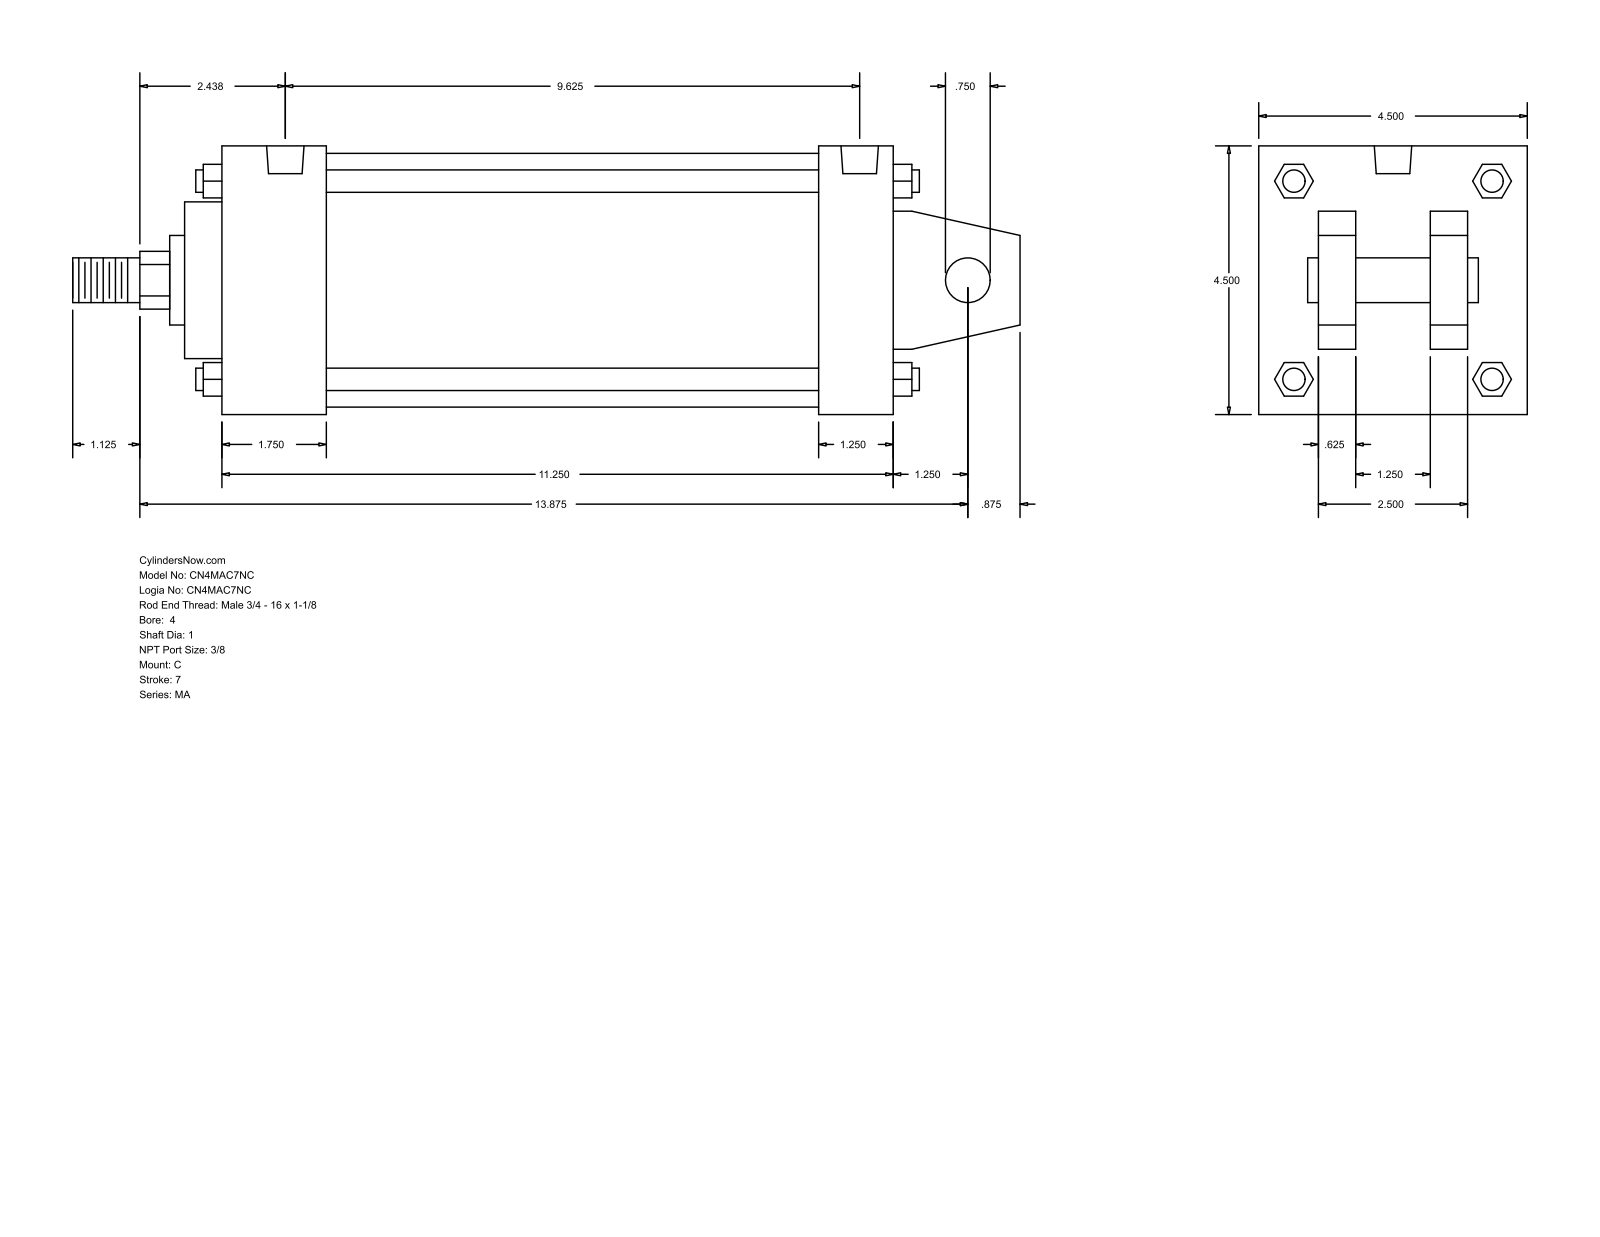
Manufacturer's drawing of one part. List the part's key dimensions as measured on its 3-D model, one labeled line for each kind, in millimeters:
Part name (STEP PRODUCT): MA_C__0400_1
STEP written by: GSSL Pune (CONFIG_CONTROL_DESIGN)
Units: millimetres
Bodies: 0 solids, 141 faces (109 planar, 32 cylindrical, 0 other)
Overall size (bounding box): 403.23 × 114.3 × 114.3
Round holes (diameter × count): ⌀11.11 ×4, ⌀15.93 ×2
Round bosses / shafts (diameter × count): ⌀9.53 ×4, ⌀19.05 ×2, ⌀107.95 ×1, ⌀66.67 ×1, ⌀38.1 ×1, ⌀25.4 ×1
Partial cylindrical surfaces — rounded edges, fillets, slot ends (radius × count): R12.29 ×1
Main face-to-face distances: 114.3, 285.76, 15.87, 73.03, 41.27, 25.4, 88.9, 47.63, 254.01, 31.75
Hole centre spacings: 234.95, 4.76, 4.77, 239.71, 239.72, 244.48
